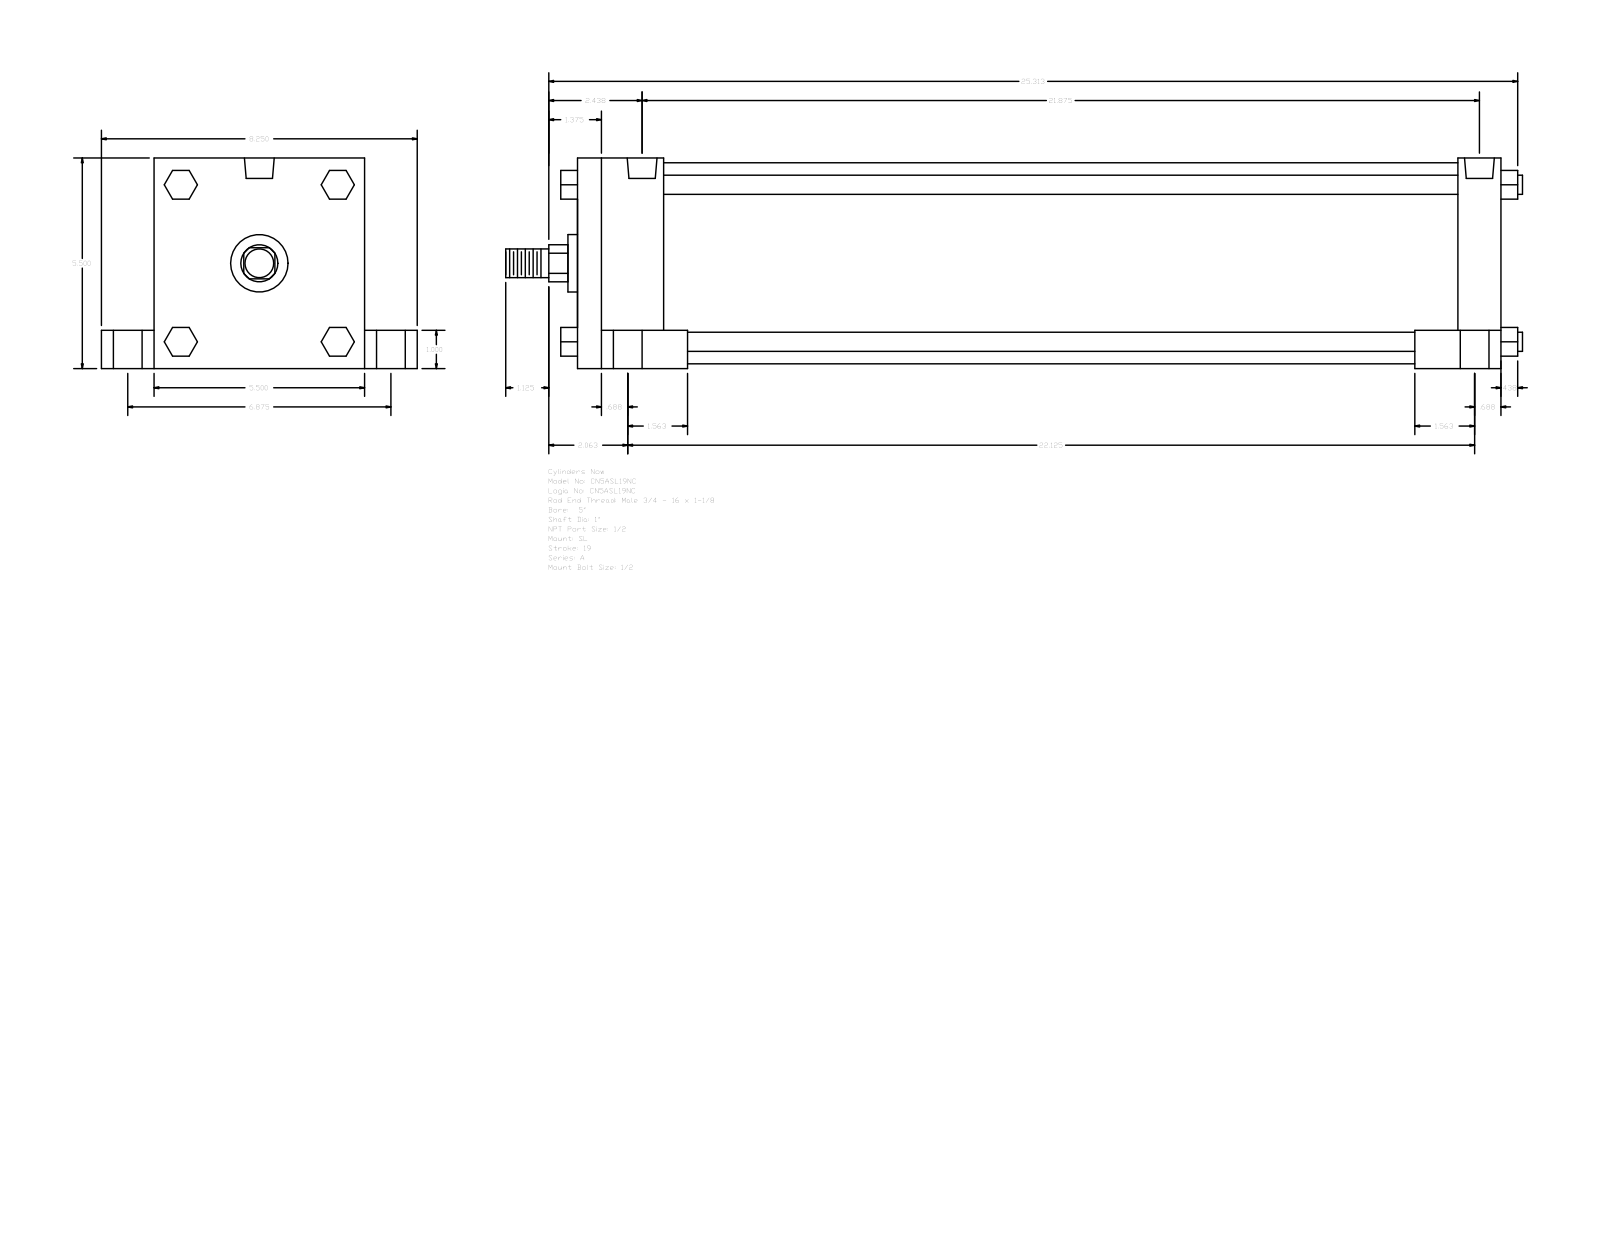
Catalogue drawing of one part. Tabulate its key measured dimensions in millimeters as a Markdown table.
| quantity | value |
| --- | --- |
| part name | A_SL__0500_1 |
| STEP written by | GSSL Pune (CONFIG_CONTROL_DESIGN) |
| units | millimeters |
| bodies | 0 solids, 150 faces (114 planar, 36 cylindrical, 0 other) |
| overall size | 674.69 × 209.55 × 139.7 |
| round holes (diameter × count) | 8.73 × 4, 19.05 × 4, 25.4 × 4, 19.77 × 2 |
| round bosses / shafts (diameter × count) | 12.7 × 4, 133.35 × 1, 38.1 × 1, 25.4 × 1, 19.05 × 1 |
| partial cylindrical surfaces (radius × count) | 12.29 × 1 |
| main face-to-face distances | 139.7, 612.78, 28.58, 25.4, 114.3, 34.93, 174.63, 57.15, 584.2, 527.05 |
| hole center spacings | 2.39, 87.31, 87.37, 87.83, 88.12, 174.62, 550.85, 553.24 |
